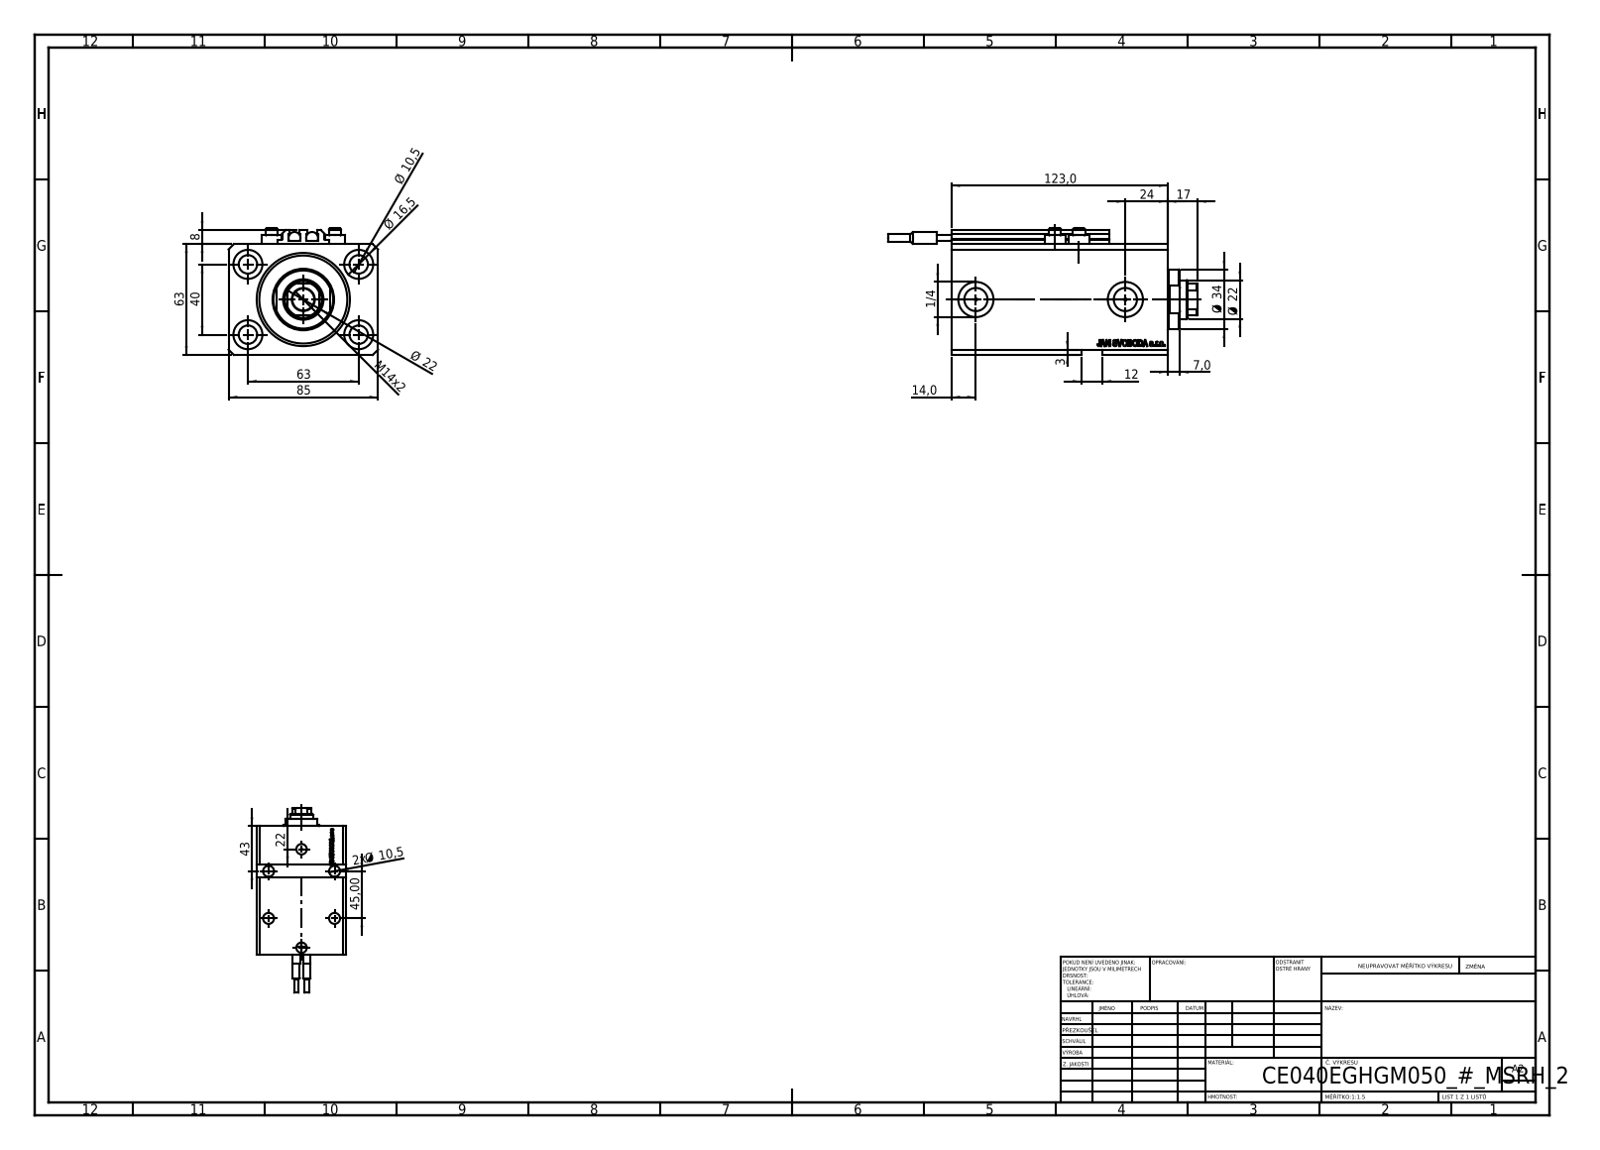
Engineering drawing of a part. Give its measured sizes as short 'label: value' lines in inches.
name: V250CE_C_VCP; ALLEN BOLT V250CE; SWITCH_V250CE; V250CE_VC_E (+1 more)
written by: SolidWorks 2019 (CONFIG_CONTROL_DESIGN)
unit: in
bodies: 10 solids, 1159 faces (567 planar, 158 cylindrical, 434 other)
size: 6.929 × 3.346 × 2.835
volume: 34.19 in³; area: 189.2 in²
holes: 8× ⌀0.413, 4× ⌀0.049, 4× ⌀0.157, 4× ⌀0.65, 2× ⌀0.394, 2× ⌀0.518, 2× ⌀0.787, 1× ⌀0.492, 1× ⌀0.866, 1× ⌀1.575, 1× ⌀2.087
bosses: 4× ⌀0.457, 4× ⌀0.276, 2× ⌀0.268, 2× ⌀0.256, 2× ⌀0.157, 1× ⌀1.339
rounds: 10× R0.008, 1× R0.413
face distances: 2.48, 3.346, 4.843, 0.669, 4.173, 0.118, 0.449, 3.724, 4.394, 2.559
hole spacings: 1.469, 2.48, 0.535, 0.606, 0.983, 1.084, 1.324, 1.417
